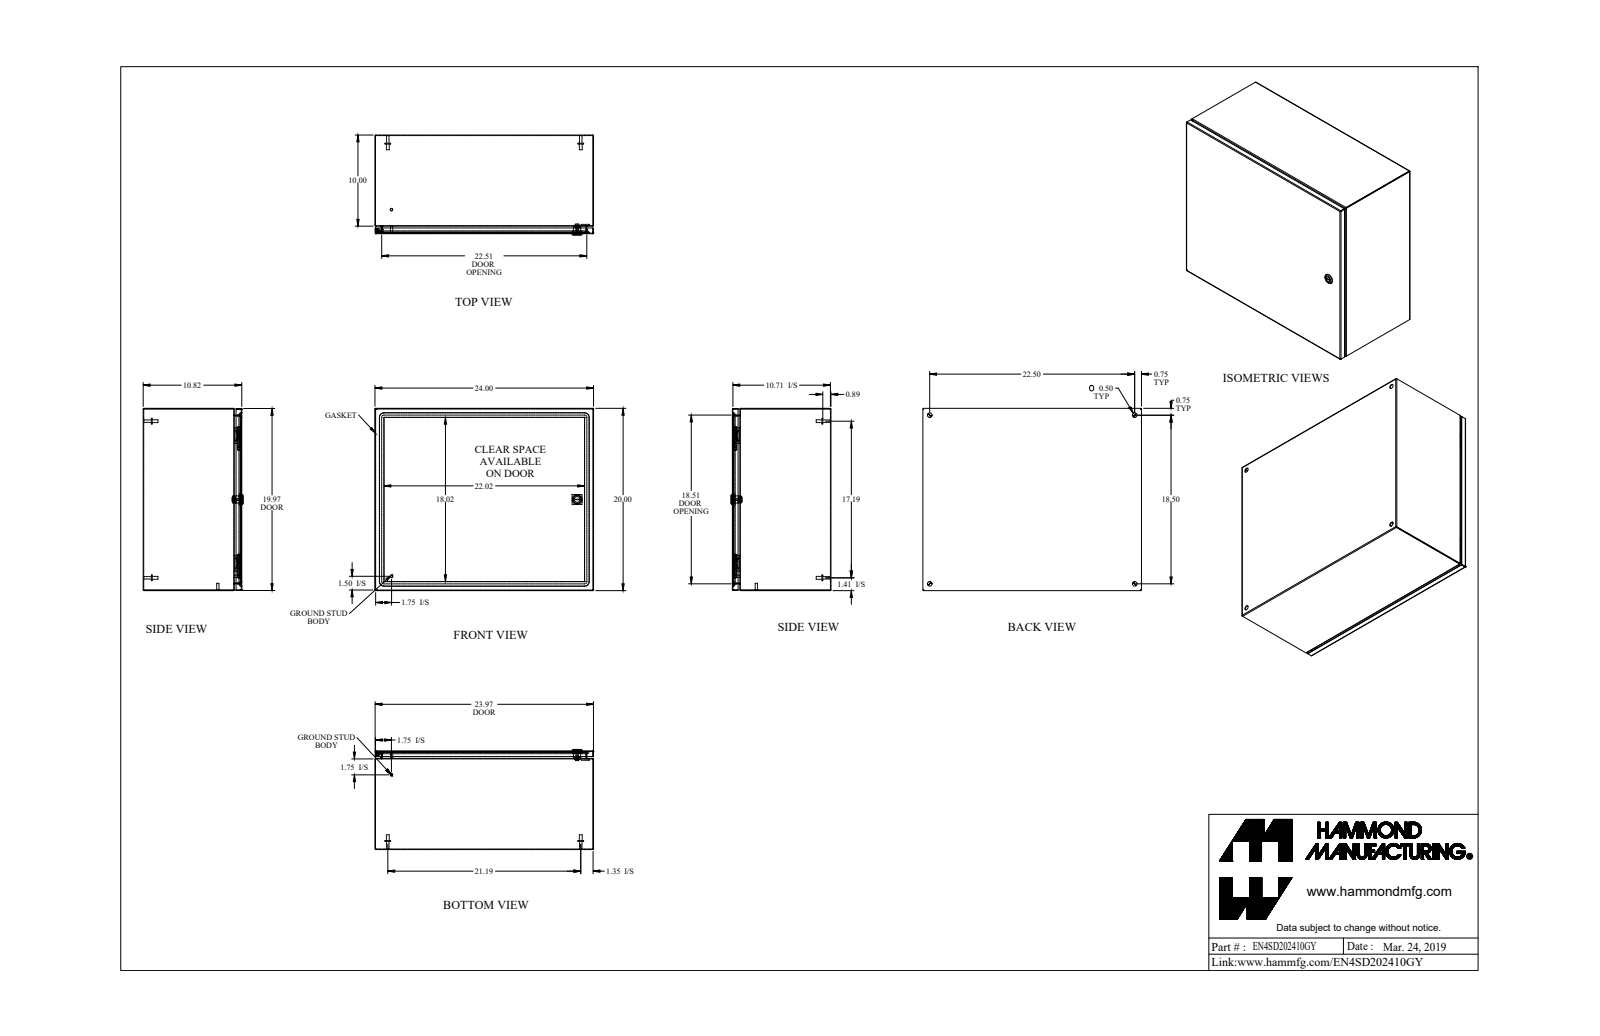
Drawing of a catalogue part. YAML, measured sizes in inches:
part_name: "EN4SD202410GY_Default"
step_written_by: "SolidWorks 2019 (CONFIG_CONTROL_DESIGN)"
units: inches
bodies: {solids: 21, faces: 634, planar: 285, cylindrical: 213, other: 136}
overall_size: [24, 20, 10.982]
volume: 123.2
surface_area: 4216
round_holes:
  - {diameter: 0.5, count: 4}
  - {diameter: 0.172, count: 1}
  - {diameter: 0.232, count: 1}
  - {diameter: 0.24, count: 1}
  - {diameter: 0.242, count: 1}
  - {diameter: 0.625, count: 1}
  - {diameter: 0.785, count: 1}
round_bosses_or_shafts:
  - {diameter: 0.625, count: 4}
  - {diameter: 0.313, count: 4}
  - {diameter: 0.27, count: 4}
  - {diameter: 0.281, count: 2}
  - {diameter: 0.25, count: 2}
  - {diameter: 1.1, count: 1}
  - {diameter: 0.525, count: 1}
  - {diameter: 0.455, count: 1}
partial_cylinders:
  - {radius: 0.029, count: 21}
  - {radius: 0.086, count: 21}
  - {radius: 0.25, count: 16}
  - {radius: 19, count: 8}
  - {radius: 0.006, count: 4}
  - {radius: 0.062, count: 4}
  - {radius: 0.499, count: 4}
  - {radius: 0.125, count: 2}
face_to_face_distances: [0.057, 10.765, 10.708, 10.822, 19.943, 23.943, 19.886, 20, 23.886, 24]
hole_center_spacings: [18.5, 22.5, 23.351, 29.129, 9.31, 9.311]
